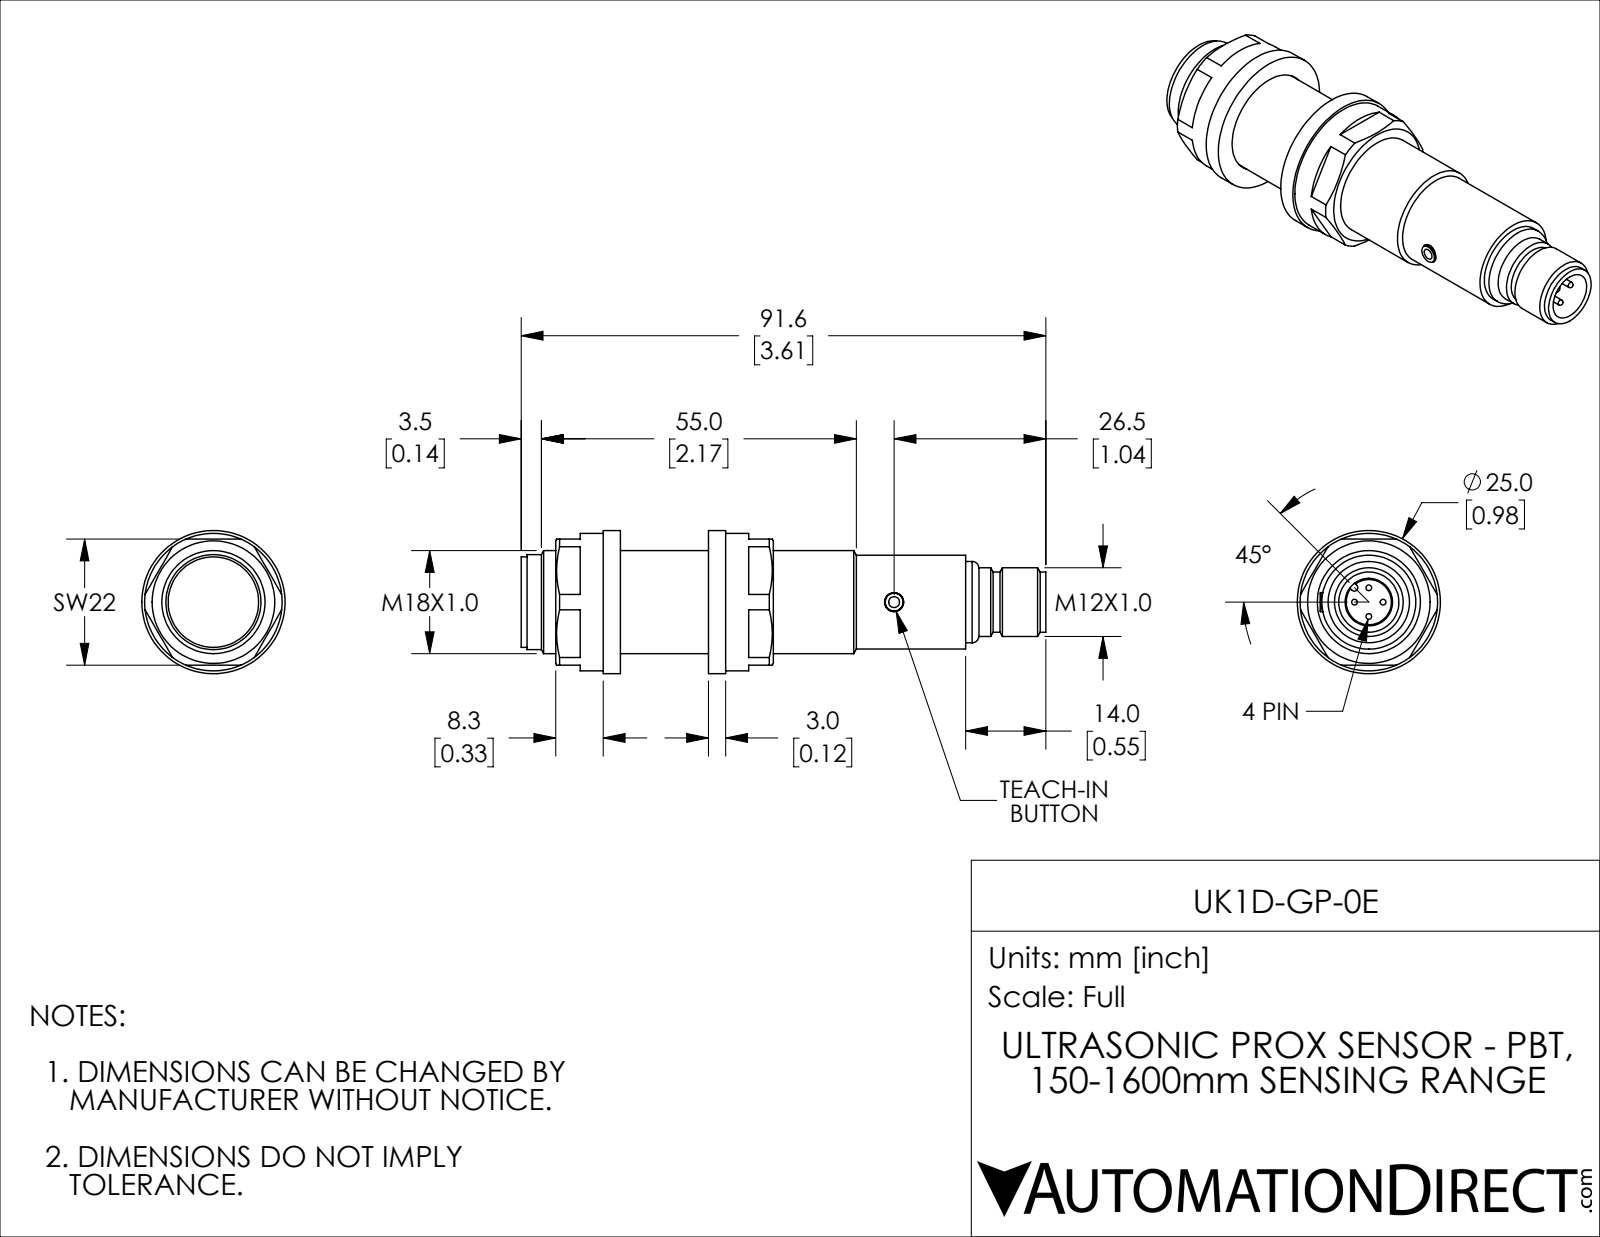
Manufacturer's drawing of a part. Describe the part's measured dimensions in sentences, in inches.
The part is named "UK1D-GP-0E". Its 3-D file was written by "SolidWorks 2018 (AUTOMOTIVE_DESIGN)". It is 6 solids with 123 faces: 43 planar, 49 cylindrical and 31 other. Overall it measures 3.606 by 0.984 by 0.984 inches. Its volume is 1.477 cubic inches and its surface area 16.01 square inches. Round holes: 1 of diameter 0.13, 1 of diameter 0.327, 1 of diameter 0.709, 1 of diameter 0.717. Round bosses or shafts: 4 of diameter 0.039, 1 of diameter 0.984, 1 of diameter 0.945, 1 of diameter 0.654, 1 of diameter 0.646, 1 of diameter 0.622, 1 of diameter 0.559, 1 of diameter 0.472. Partial cylindrical surfaces (rounded edges, fillets, slot ends): 1 of radius 0.024. The main face-to-face distances are 0.118, 0.724, 0.843, 0.606, 0.866, 0.327, 0.445, 1.051, 1.169, 0.563.
